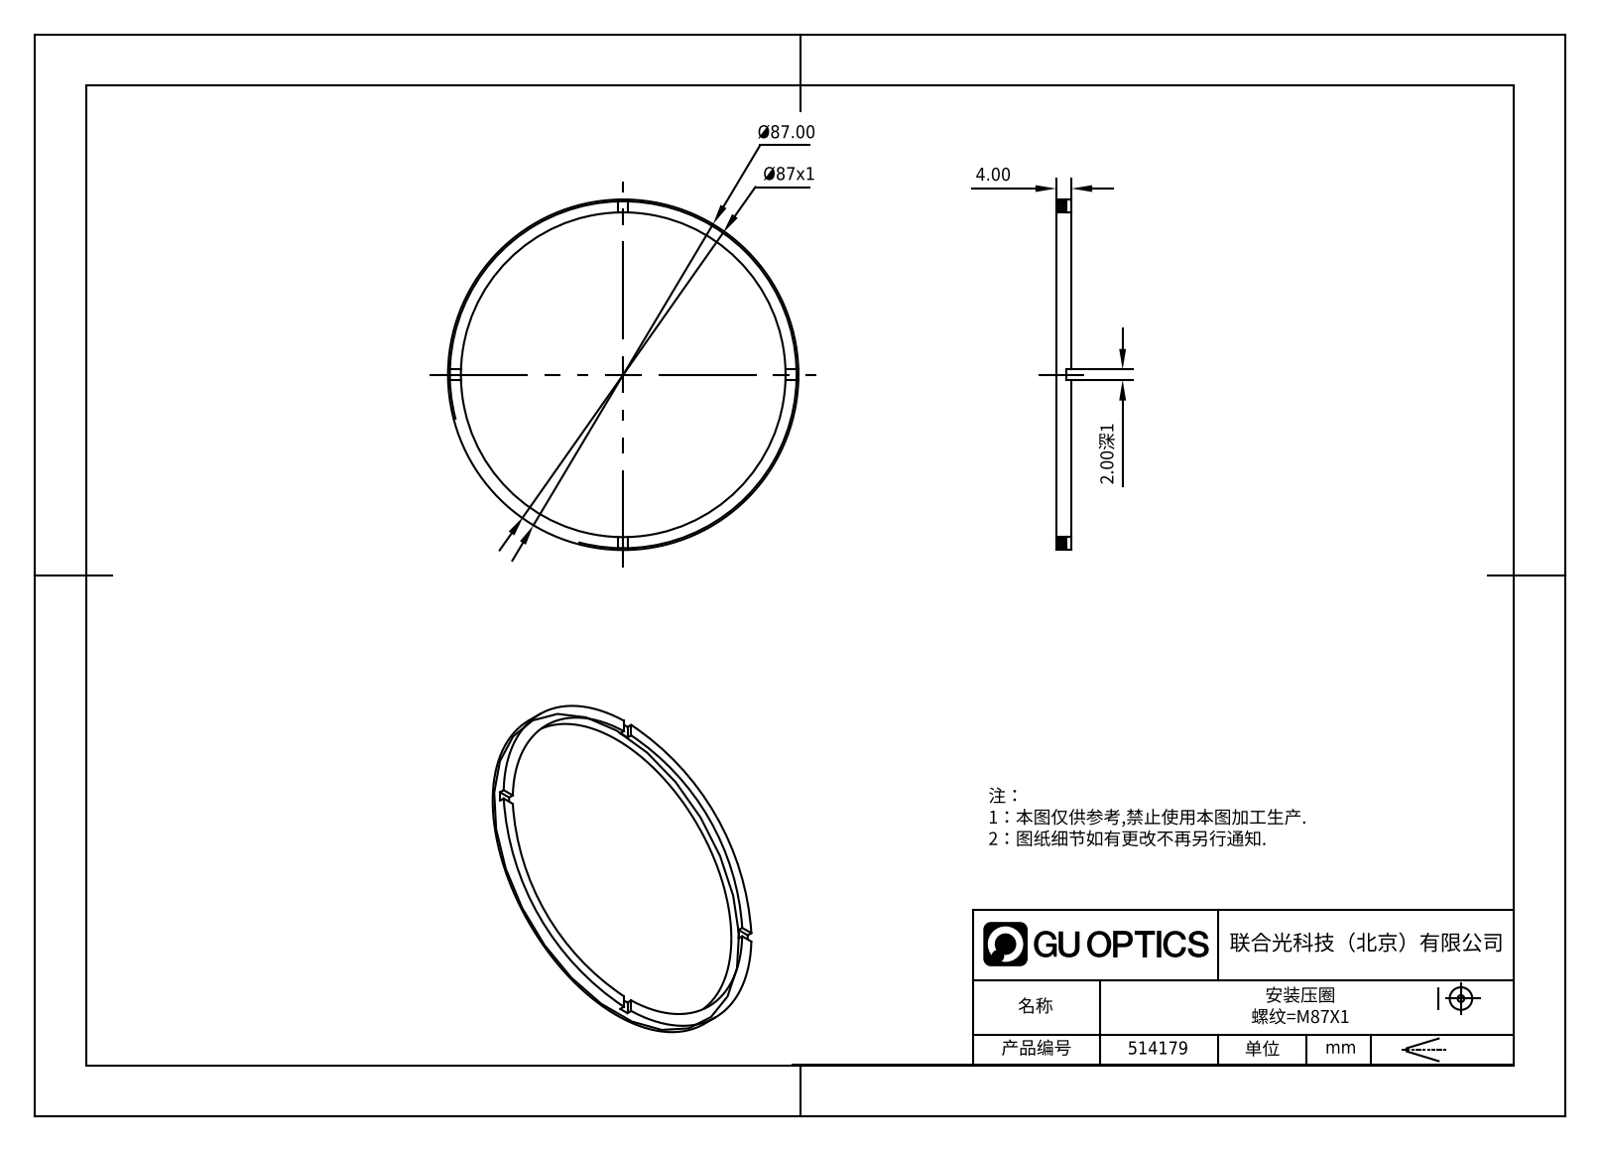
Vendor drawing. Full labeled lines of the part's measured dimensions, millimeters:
Part name (STEP PRODUCT): 514179
STEP written by: SolidWorks 2020 (CONFIG_CONTROL_DESIGN)
Units: millimetres
Bodies: 1 solid, 21 faces (17 planar, 4 cylindrical, 0 other)
Overall size (bounding box): 87 × 87 × 4
Volume: 3 143 mm³ · Surface area: 3 703 mm²
Round holes (diameter × count): ⌀81 ×1
Round bosses / shafts (diameter × count): ⌀87 ×1
Main face-to-face distances: 4, 3, 1, 2
